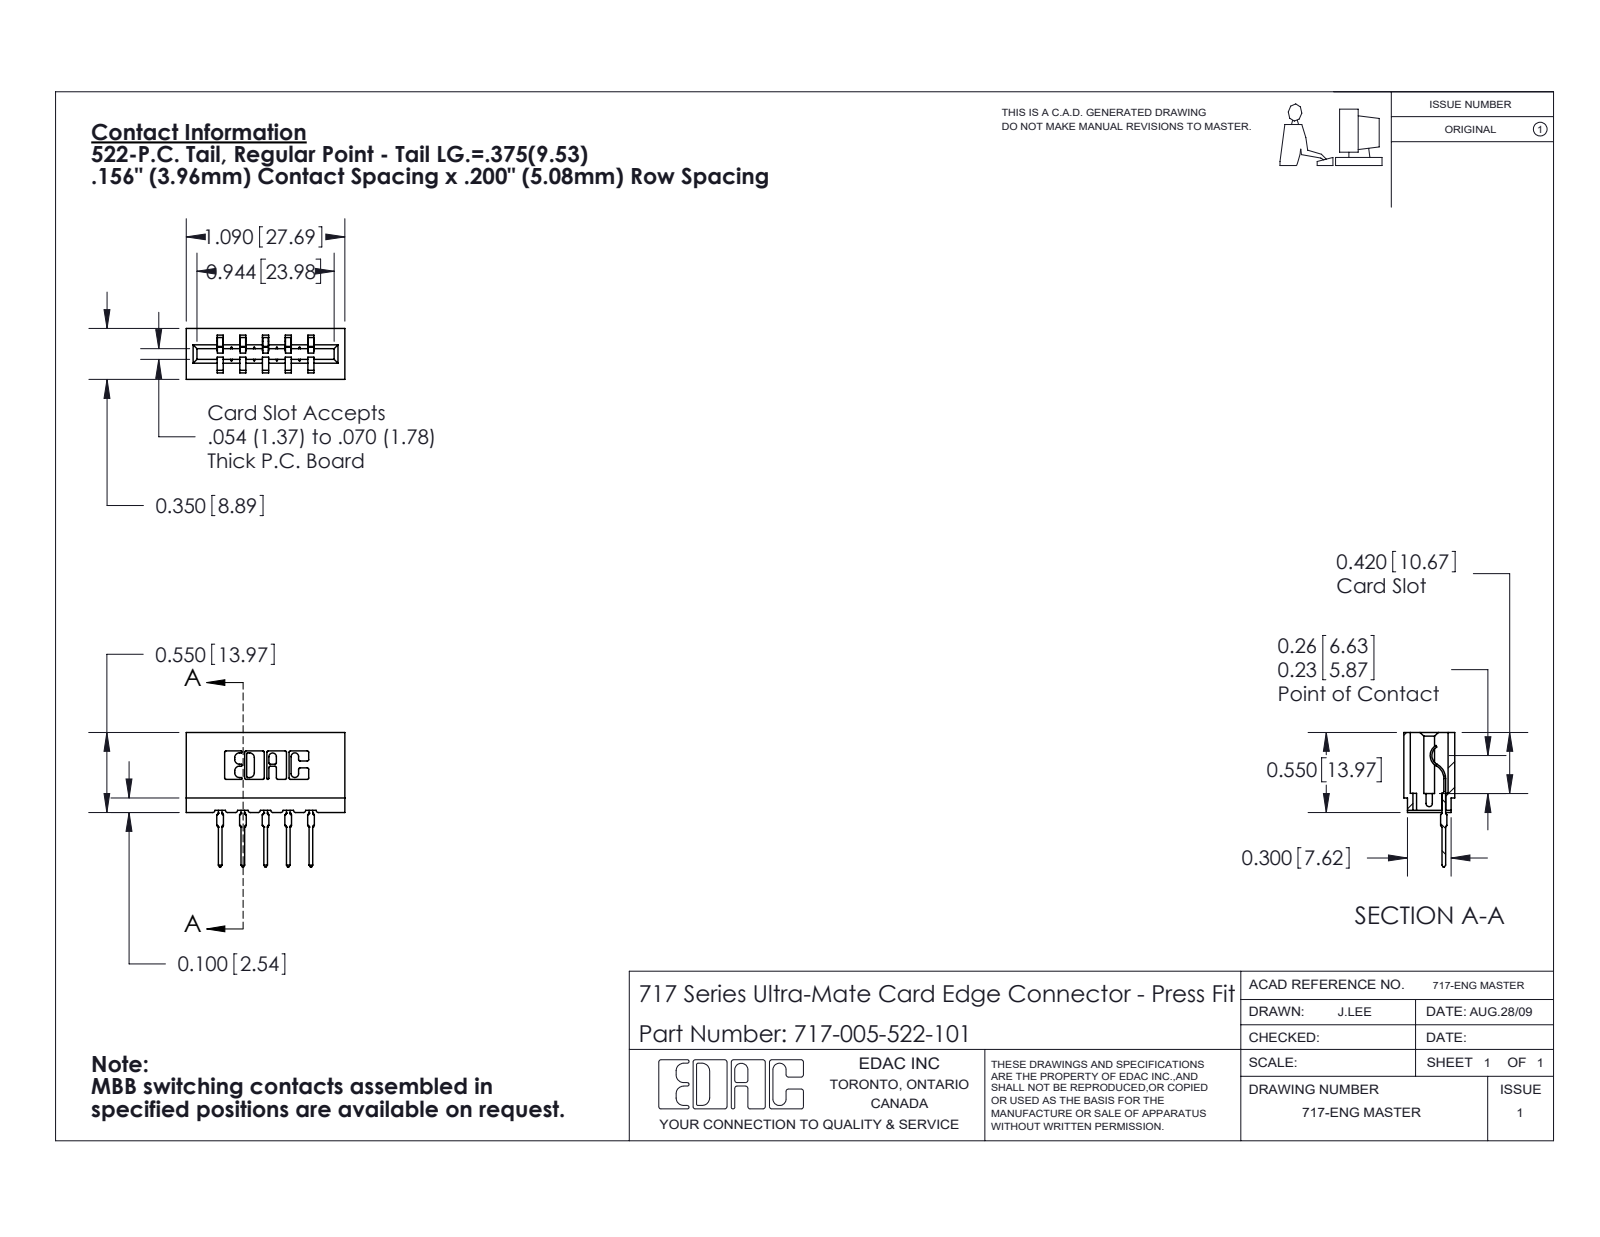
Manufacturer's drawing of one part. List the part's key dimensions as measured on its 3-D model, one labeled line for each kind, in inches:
Part name (STEP PRODUCT): 717 Part_Insulator Option - 06; 745-292-001_522; 717-005-522-101
STEP written by: SolidWorks 2020 (CONFIG_CONTROL_DESIGN)
Units: inches
Bodies: 6 solids, 659 faces (394 planar, 135 cylindrical, 130 other)
Overall size (bounding box): 1.09 × 0.924 × 0.35
Volume: 0.153 in³ · Surface area: 4.855 in²
Partial cylindrical surfaces — rounded edges, fillets, slot ends (radius × count): R0.01 ×22, R0.015 ×10, R0.021 ×10, R0.007 ×6, R0.031 ×6, R0.005 ×4, R0.011 ×4, R0.026 ×3
Main face-to-face distances: 0.212, 0.156, 0.138, 0.35, 0.198, 0.042, 0.312, 0.312, 0.468, 0.074
